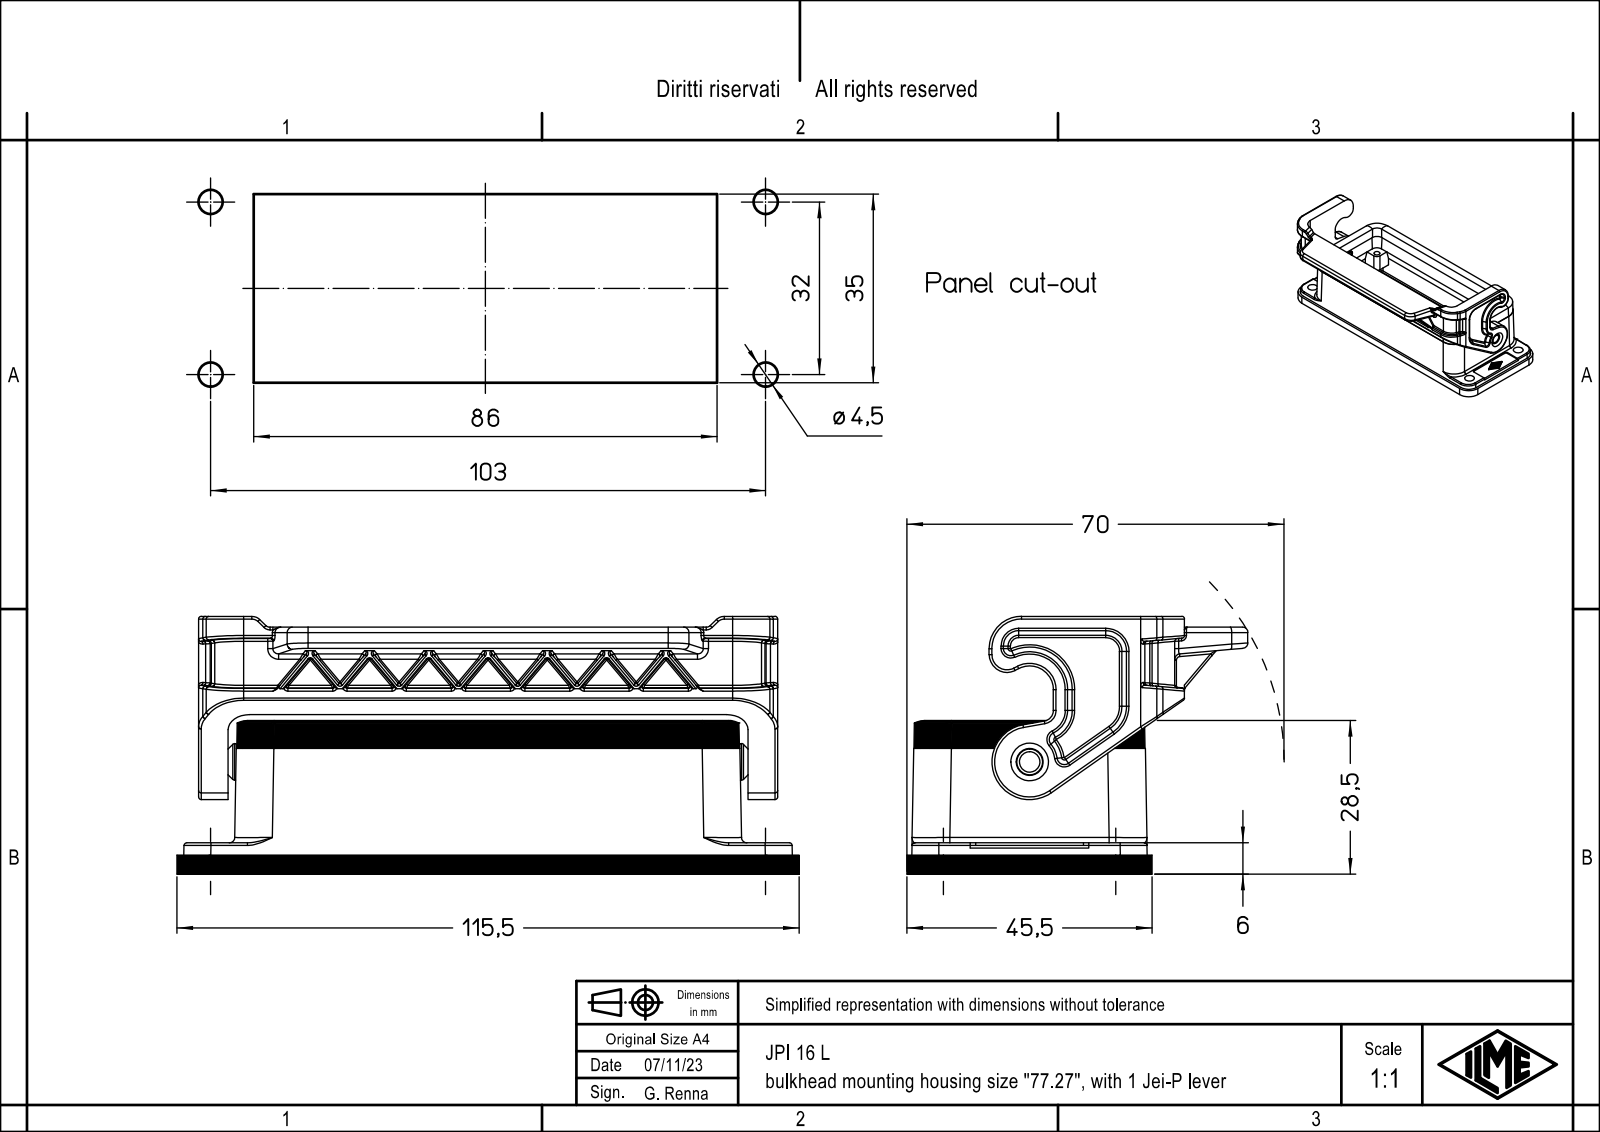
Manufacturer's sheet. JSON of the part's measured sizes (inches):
{"part_name": "JPI 16 L", "step_written_by": "Creo Elements/Direct Modeling 20.1B 02-Apr-2019 (C) Parametric Technology GmbH (AUTOMOTIVE_DESIGN)", "units": "inches", "bodies": {"solids": 1, "faces": 842, "planar": 237, "cylindrical": 323, "other": 282}, "overall_size": [4.547, 2.49, 1.882], "volume_in3": 2.985, "surface_area_in2": 49.94, "round_holes": [[0.15, 4], [0.177, 4], [0.189, 1]], "round_bosses_or_shafts": [[0.268, 1]], "partial_cylinders_radius": [[0.012, 99], [0.02, 63], [0.039, 17], [0.157, 16], [0.007, 15], [0.079, 9], [0.276, 9], [0.118, 8]], "face_to_face_distances": [0.119, 0.138, 1.803, 0.079, 3.799, 1.594, 0.039, 0.157, 1.415, 1.534], "hole_center_spacings": [1.26, 4.055, 4.246]}
